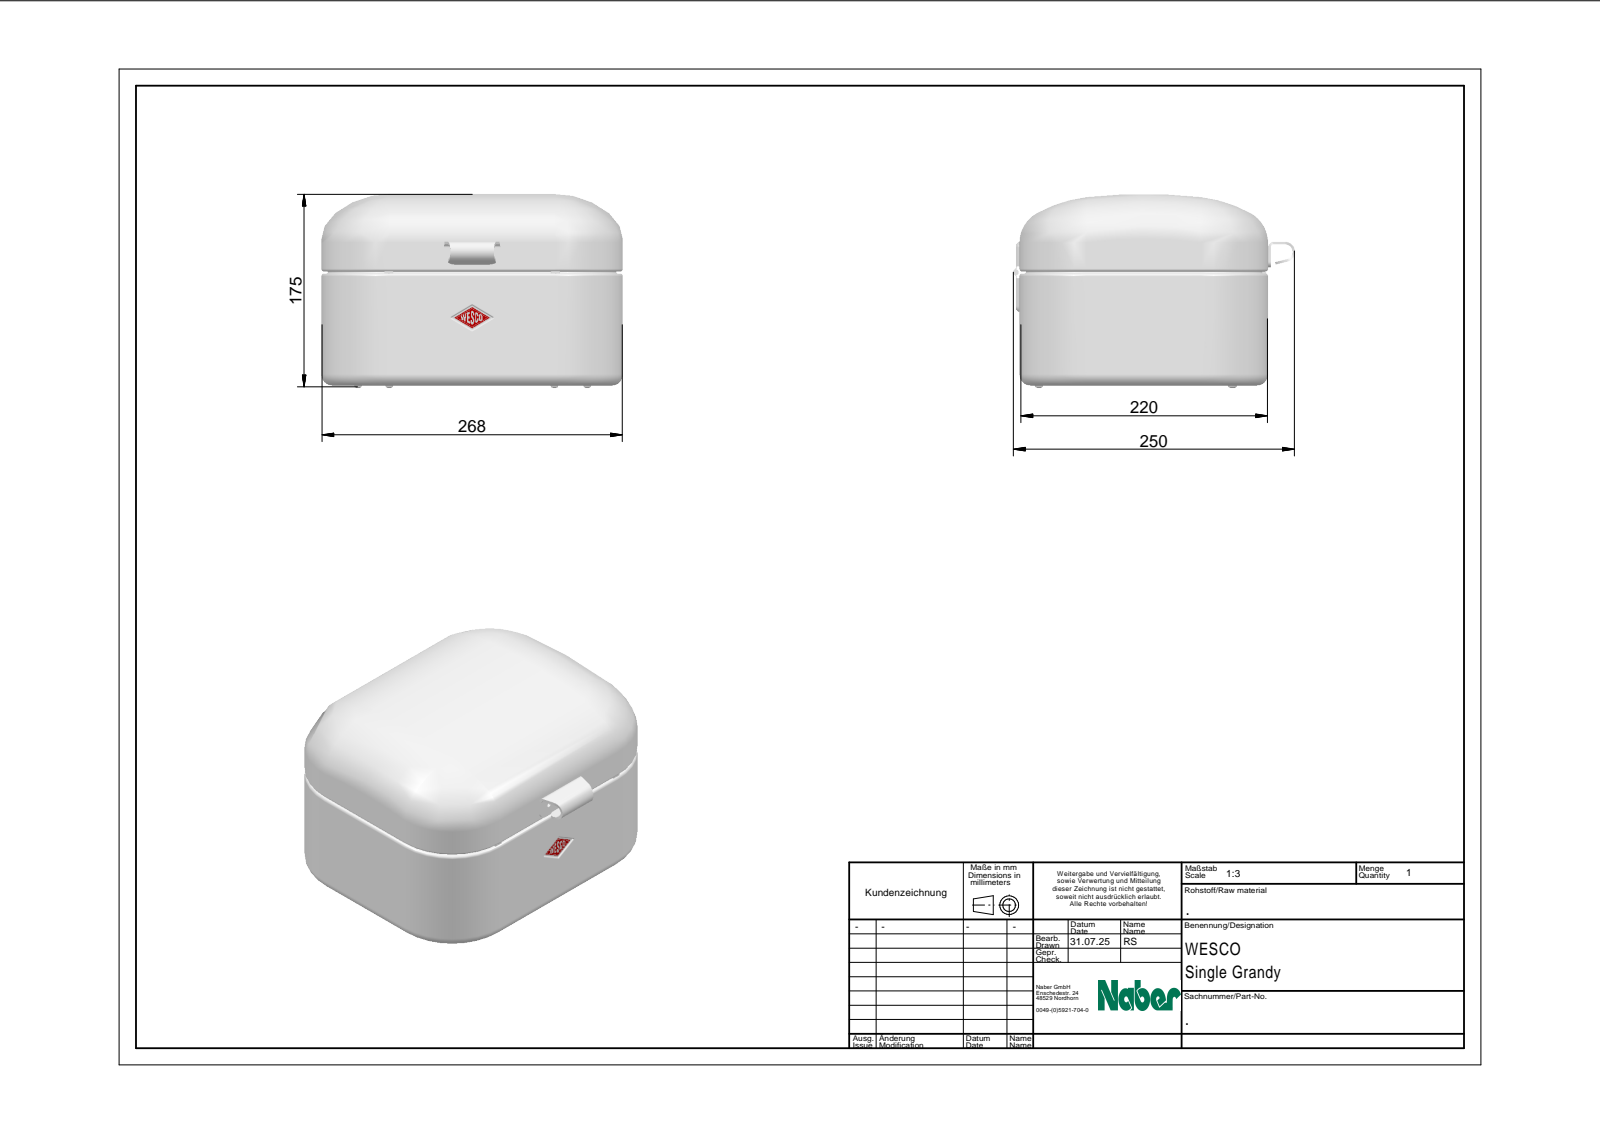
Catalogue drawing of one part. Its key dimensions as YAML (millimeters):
part_name: "235101-2X_ASM|1887XG#1887XG;1887XG"
step_written_by: "Spatial InterOp 3D (AUTOMOTIVE_DESIGN)"
units: millimeters
bodies: {solids: 5, faces: 818, planar: 252, cylindrical: 278, other: 288}
overall_size: [269.12, 268, 216.51]
volume: 261589
surface_area: 515668
round_holes:
  - {diameter: 4.5, count: 18}
  - {diameter: 2.5, count: 14}
  - {diameter: 4.2, count: 2}
round_bosses_or_shafts:
  - {diameter: 6.5, count: 10}
  - {diameter: 3, count: 2}
  - {diameter: 2, count: 2}
  - {diameter: 5.4, count: 1}
  - {diameter: 3.4, count: 1}
partial_cylinders:
  - {radius: 0.5, count: 16}
  - {radius: 1, count: 14}
  - {radius: 1.5, count: 13}
  - {radius: 2.5, count: 9}
  - {radius: 59, count: 8}
  - {radius: 60, count: 8}
  - {radius: 1.3, count: 6}
  - {radius: 5, count: 5}
face_to_face_distances: [1, 219.96, 267, 218.96, 220.96, 266, 268, 2.96, 222.92, 5.8]
hole_center_spacings: [6, 10.4, 110, 22, 32.5, 34.93, 39.25, 40.45]
